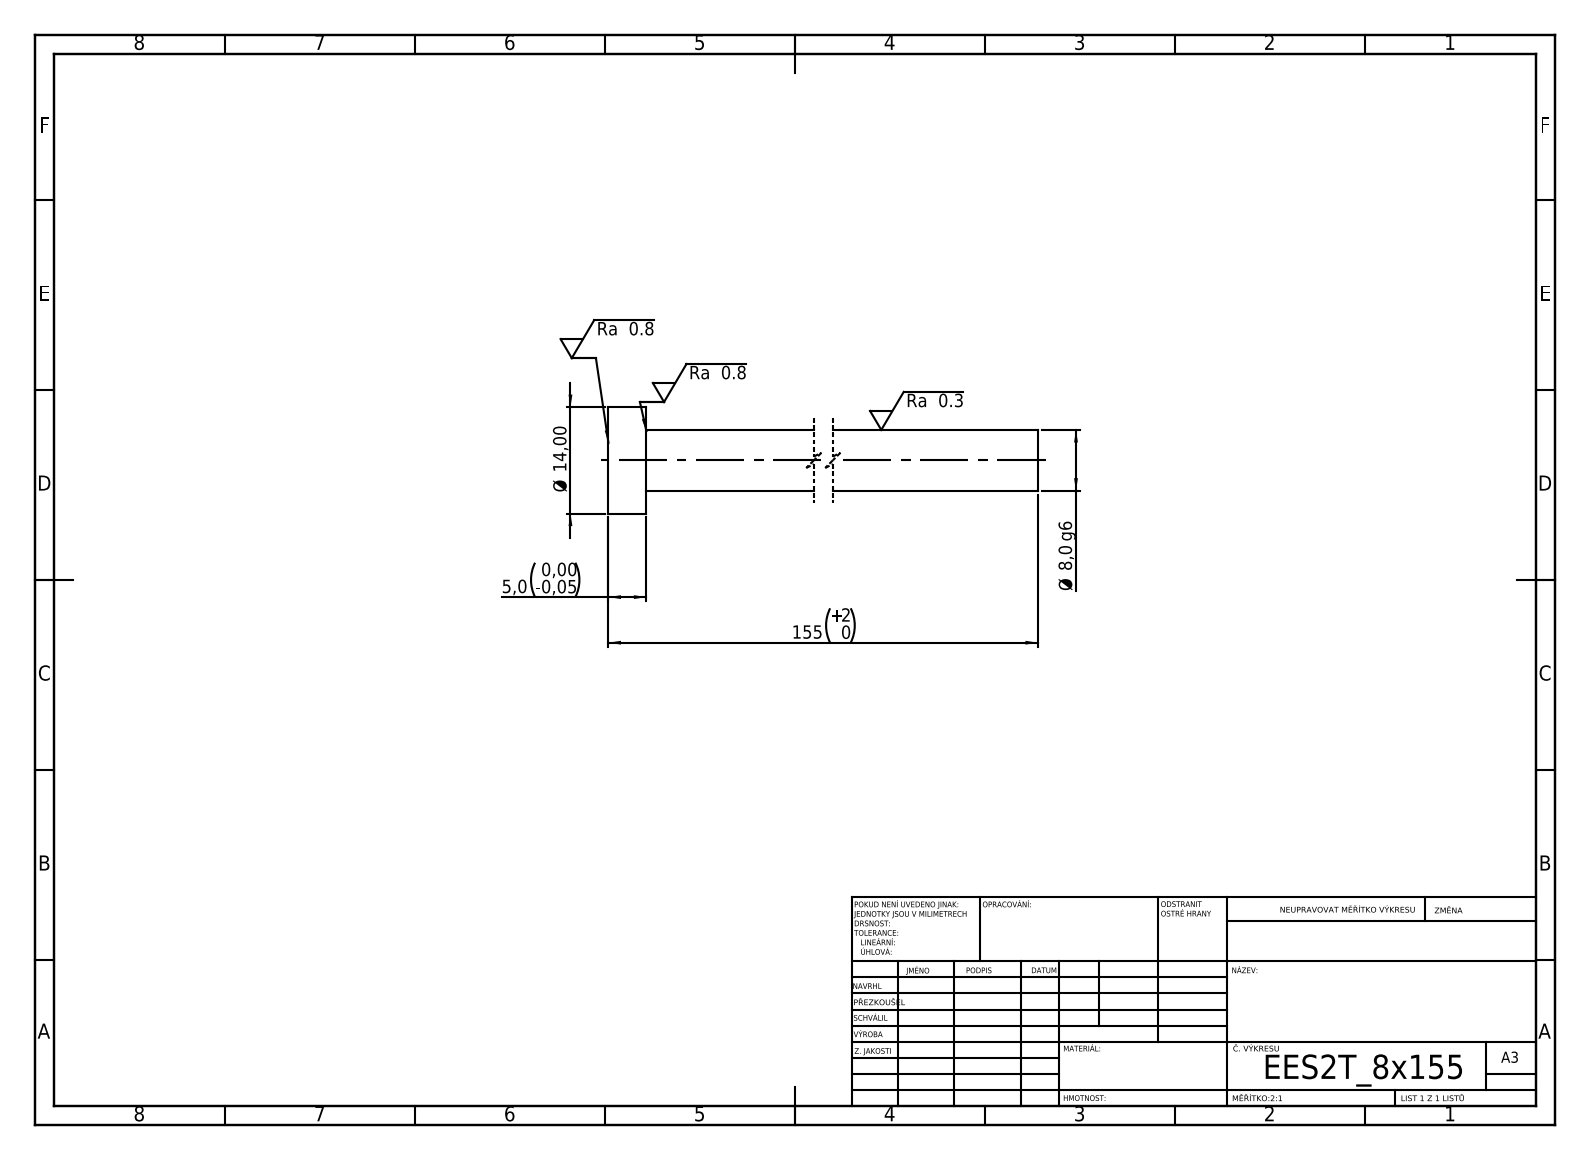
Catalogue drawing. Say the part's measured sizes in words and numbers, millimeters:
Its 3-D file was written by "SolidWorks 2019 (CONFIG_CONTROL_DESIGN)". It is 1 solid with 7 faces: 3 planar, 4 cylindrical and 0 other. Overall it measures 155 by 14 by 14 millimeters. Its volume is 8 310 cubic millimeters and its surface area 4 298 square millimeters. Round bosses or shafts: 1 of diameter 14, 1 of diameter 8. The main face-to-face distances are 5, 155, 150.
